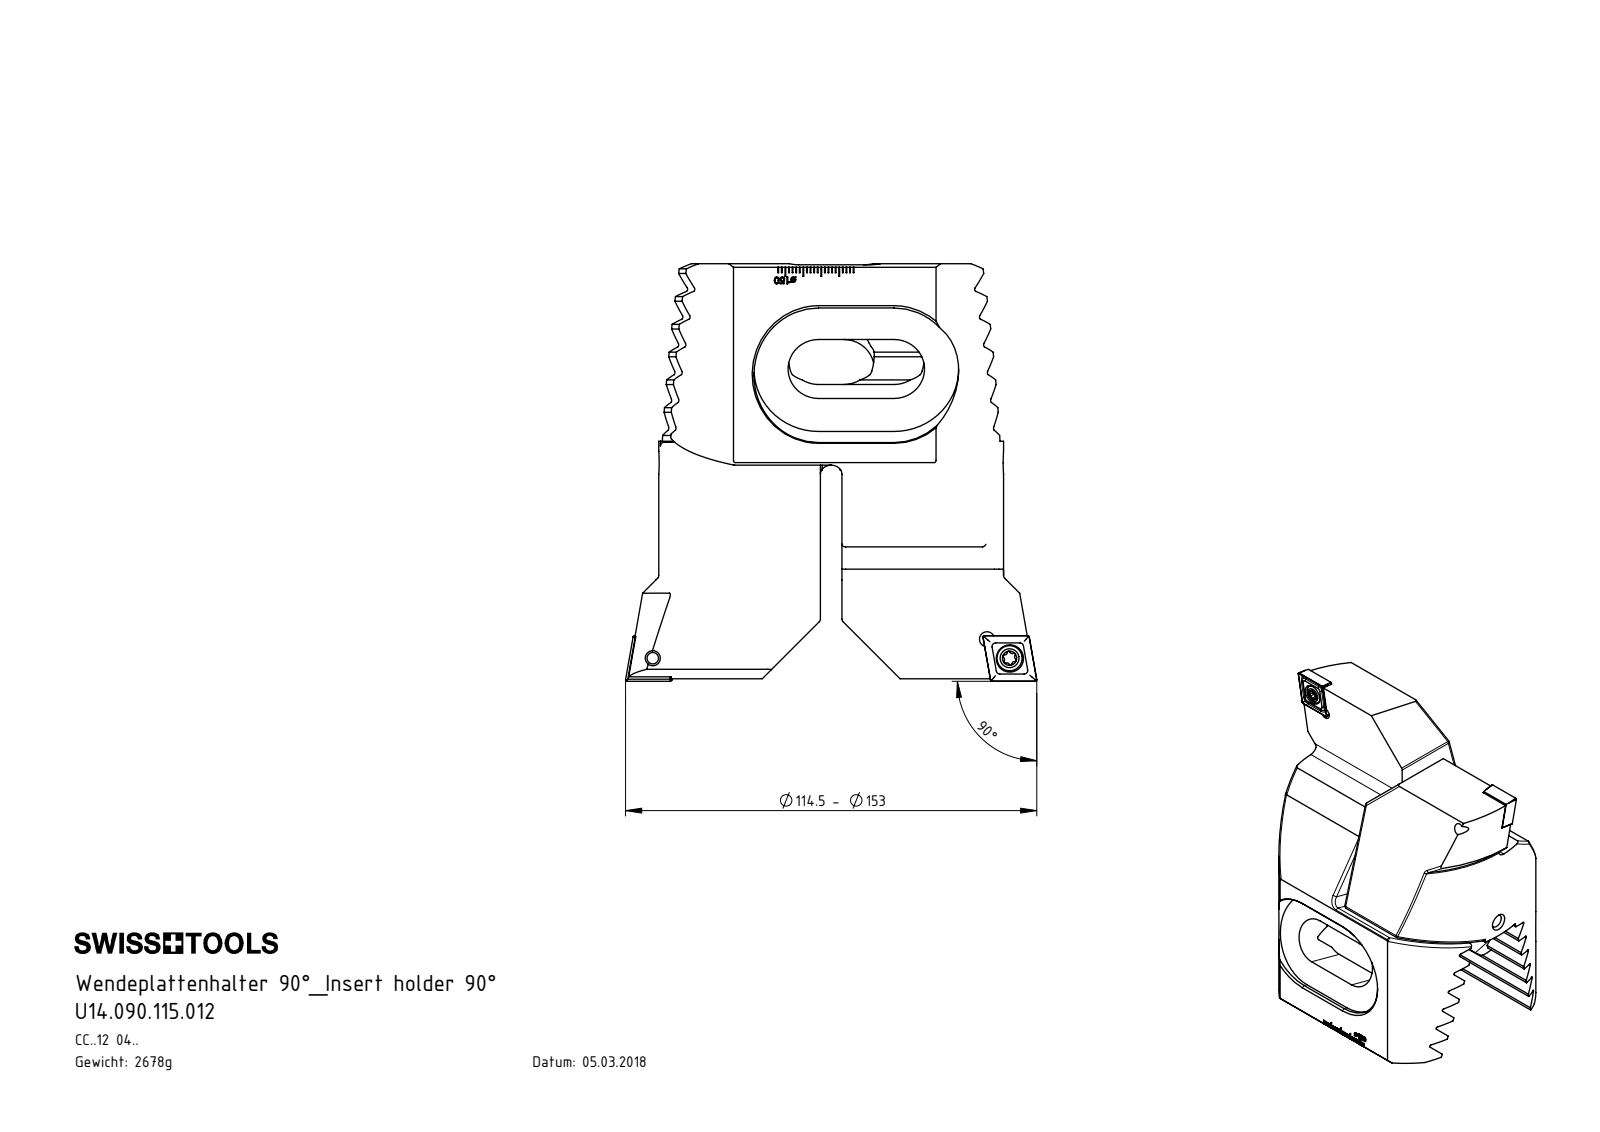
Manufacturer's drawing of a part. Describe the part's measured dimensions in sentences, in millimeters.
The part is named "Z94-xxx.001.067_E; Z94.WCC.B11.067; WCC-ER2.001.010_A; CCMT120404 (+1 more)". Its 3-D file was written by "SolidWorks 2017 (AUTOMOTIVE_DESIGN)". It is 8 solids with 716 faces: 444 planar, 102 cylindrical and 170 other. Overall it measures 116.2 by 114.5 by 75.2 millimeters. Its volume is 342 967 cubic millimeters and its surface area 64 409 square millimeters. Round holes: 4 of diameter 4.2, 2 of diameter 2, 2 of diameter 5.5, 2 of diameter 7.6, 1 of diameter 5. Round bosses or shafts: 2 of diameter 7, 2 of diameter 5, 1 of diameter 6, 1 of diameter 4. Partial cylindrical surfaces (rounded edges, fillets, slot ends): 16 of radius 1, 12 of radius 0.39, 12 of radius 0.58, 6 of radius 0.69, 6 of radius 0.69, 6 of radius 3, 4 of radius 8.5, 4 of radius 12. The main face-to-face distances are 6.93, 20.78, 27.71, 13.85, 13.86, 13.19, 37.3, 37.9, 6.92, 6. The hole center spacings are 8.21, 8.33, 25, 93.2, 93.29, 99.43, 48.3, 86.76.
